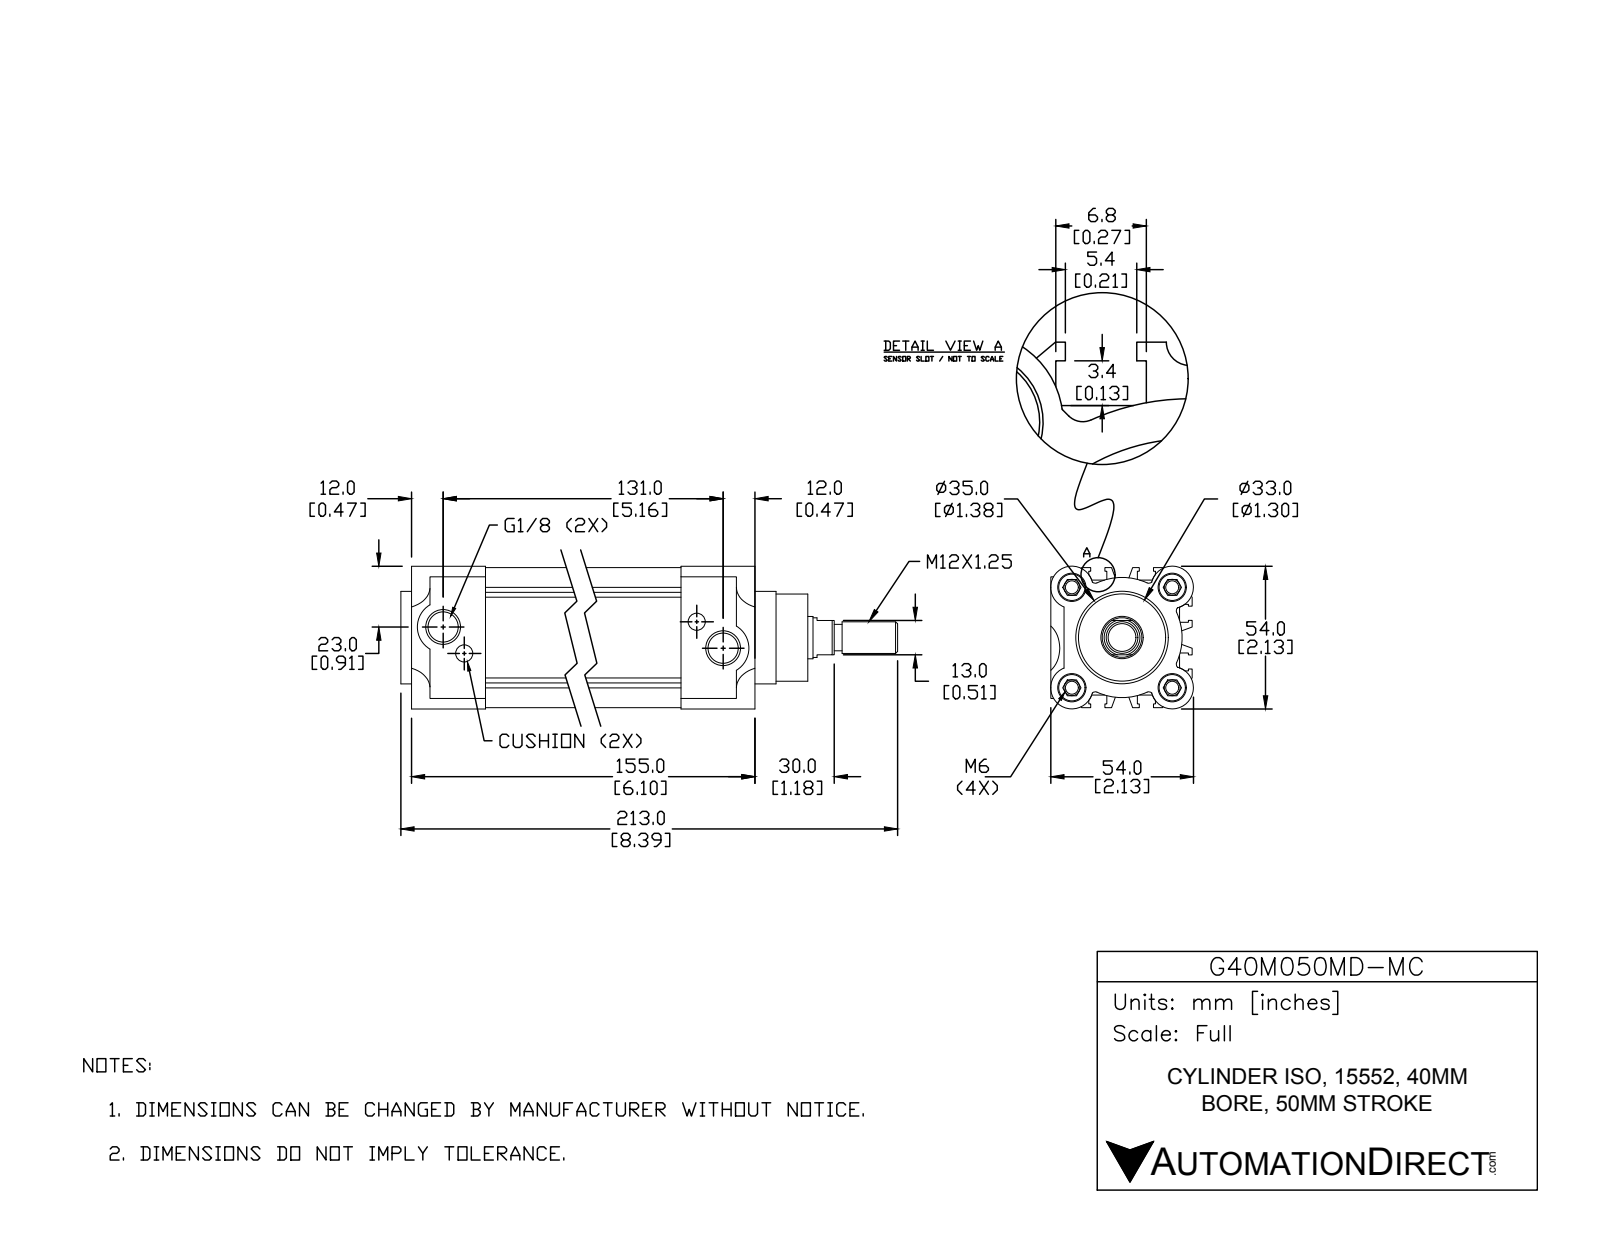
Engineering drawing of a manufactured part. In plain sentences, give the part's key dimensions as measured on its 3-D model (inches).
The part is named "40-50-83-B; G40M050MD-MC; 40121-HR; 40-HL (+1 more)". Its 3-D file was written by "SolidWorks 2015 (CONFIG_CONTROL_DESIGN)". It is 4 solids with 418 faces: 236 planar, 138 cylindrical and 44 other. Overall it measures 8.386 by 2.126 by 2.126 inches. Its volume is 21.16 cubic inches and its surface area 155.6 square inches. Round holes: 4 of diameter 0.194, 4 of diameter 0.421, 2 of diameter 0.256, 2 of diameter 0.451, 1 of diameter 0.63. Round bosses or shafts: 5 of diameter 0.394, 1 of diameter 1.575, 1 of diameter 1.378, 1 of diameter 1.299, 1 of diameter 0.591, 1 of diameter 0.472. Partial cylindrical surfaces (rounded edges, fillets, slot ends): 12 of radius 0.059, 6 of radius 0.004, 4 of radius 0.295, 4 of radius 0.315, 2 of radius 0.384, 1 of radius 0.886, 1 of radius 0.896. The main face-to-face distances are 1.9, 0.187, 3.622, 0.276, 1.378, 3.898, 2.087, 0.724, 0.02, 0.547. The hole center spacings are 1.058, 1.496, 2.116, 0.504, 0.557, 4.474, 4.765, 4.843.
